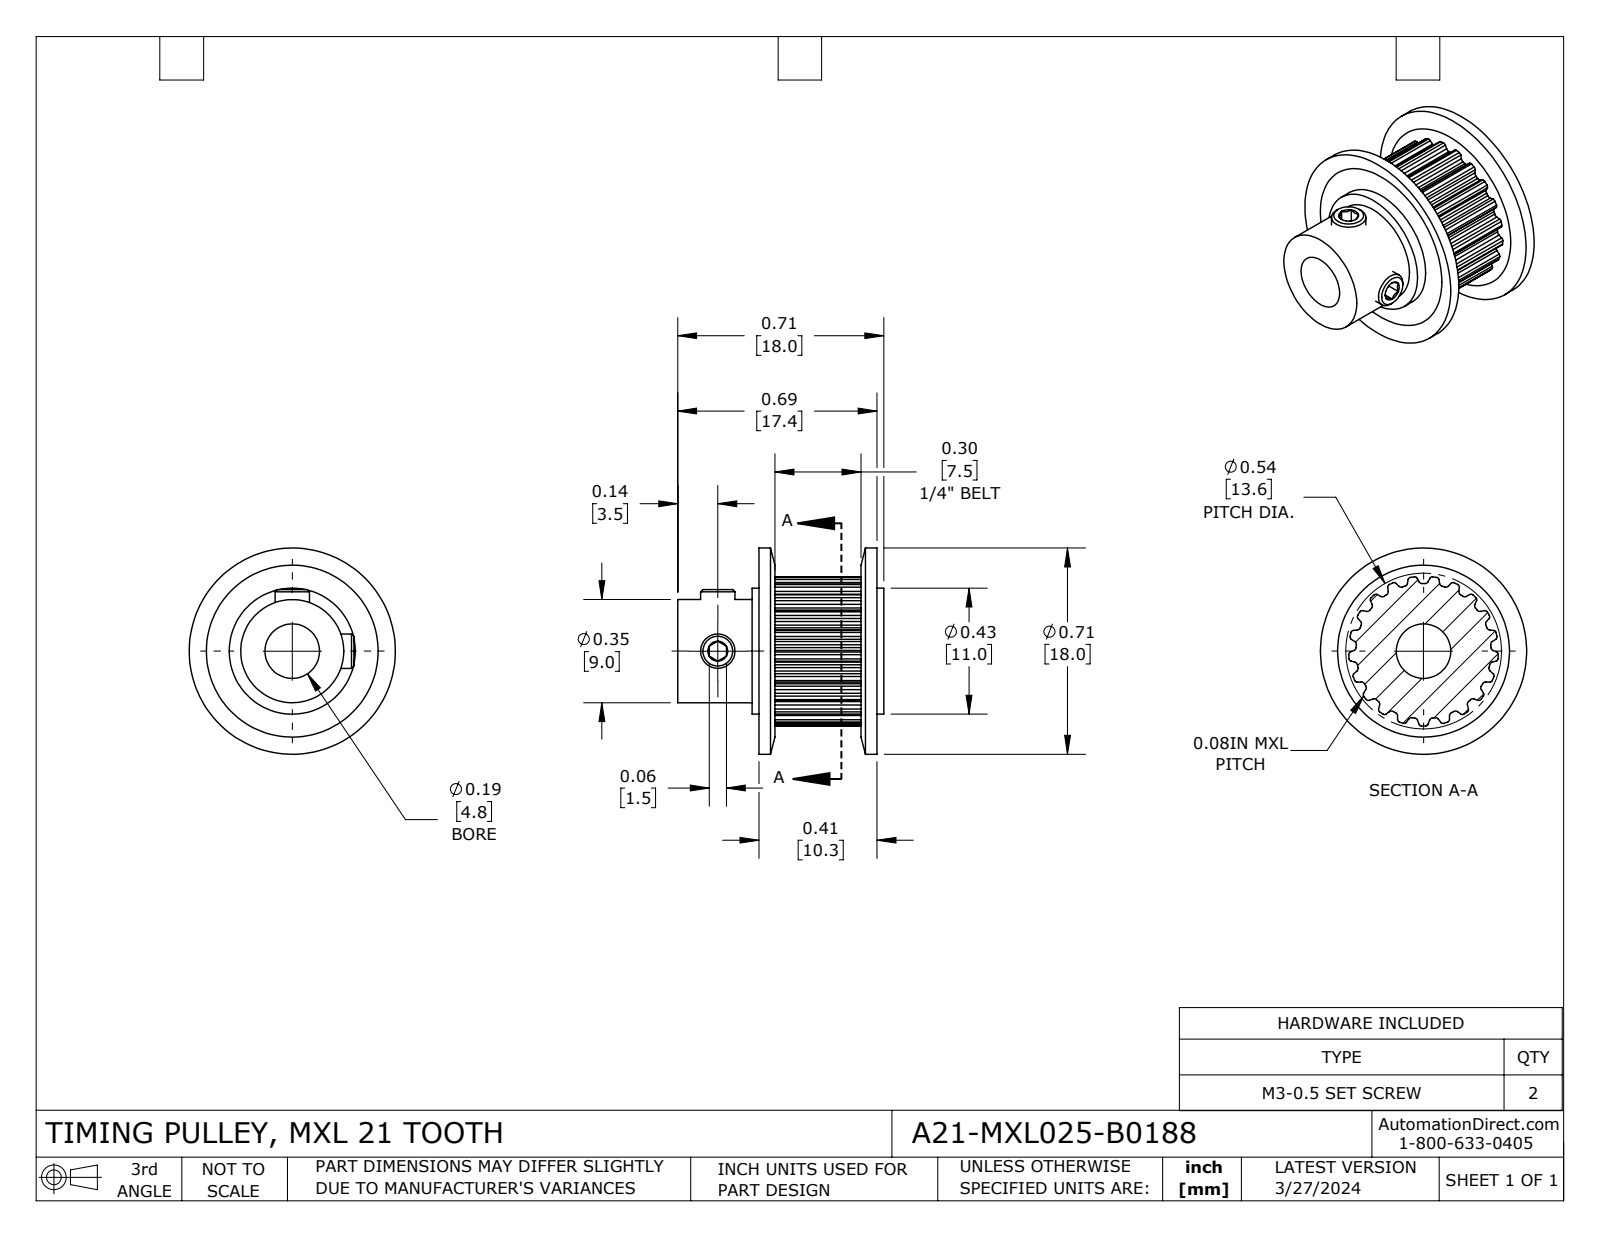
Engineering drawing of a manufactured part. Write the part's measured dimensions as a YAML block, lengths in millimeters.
part_name: "A21-MXL025-B0188"
step_written_by: "SolidWorks 2021 (CONFIG_CONTROL_DESIGN)"
units: millimeters
bodies: {solids: 5, faces: 266, planar: 67, cylindrical: 165, other: 34}
overall_size: [18, 18, 18]
volume: 1718
surface_area: 2133
round_holes:
  - {diameter: 2.5, count: 2}
  - {diameter: 4.76, count: 1}
  - {diameter: 11, count: 1}
round_bosses_or_shafts:
  - {diameter: 3, count: 2}
  - {diameter: 18, count: 1}
  - {diameter: 9, count: 1}
partial_cylinders:
  - {radius: 0.23, count: 42}
  - {radius: 0.3, count: 42}
  - {radius: 5.89, count: 1}
  - {radius: 6.54, count: 1}
face_to_face_distances: [1, 8.5, 9.5, 7.5, 2, 10.5, 18, 17, 16, 11.5]
